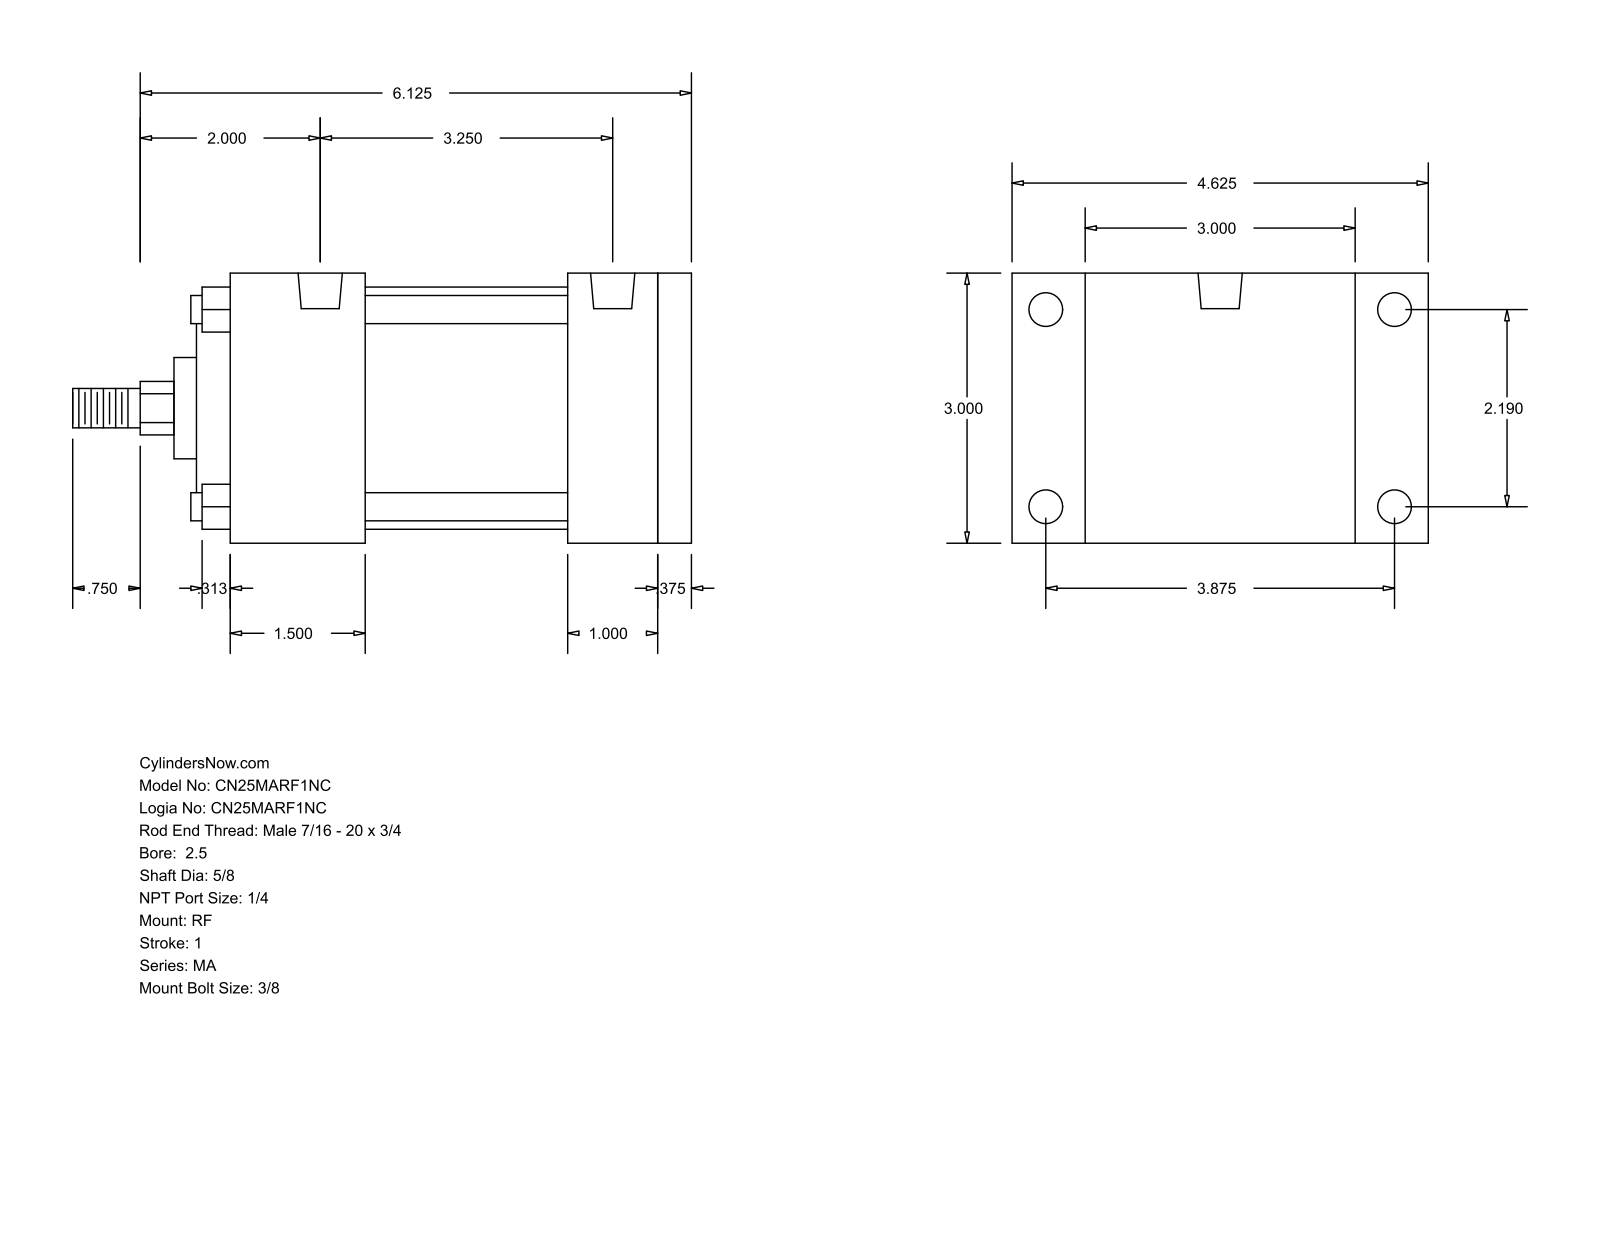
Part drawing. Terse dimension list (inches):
name: MA_RF__0250_0.625
written by: GSSL Pune (CONFIG_CONTROL_DESIGN)
unit: in
bodies: 0 solids, 94 faces (65 planar, 29 cylindrical, 0 other)
size: 6.875 × 4.625 × 3
holes: 4× ⌀0.313, 4× ⌀0.375, 2× ⌀0.492
bosses: 4× ⌀0.313, 1× ⌀2.69, 1× ⌀2, 1× ⌀1.125, 1× ⌀0.625, 1× ⌀0.437
rounds: 1× R0.297
face distances: 3, 5.125, 0.375, 4.75, 1, 3.25, 2.25, 1.5, 3.75, 3.625
hole spacings: 2.19, 3.25, 3.875, 4.451
